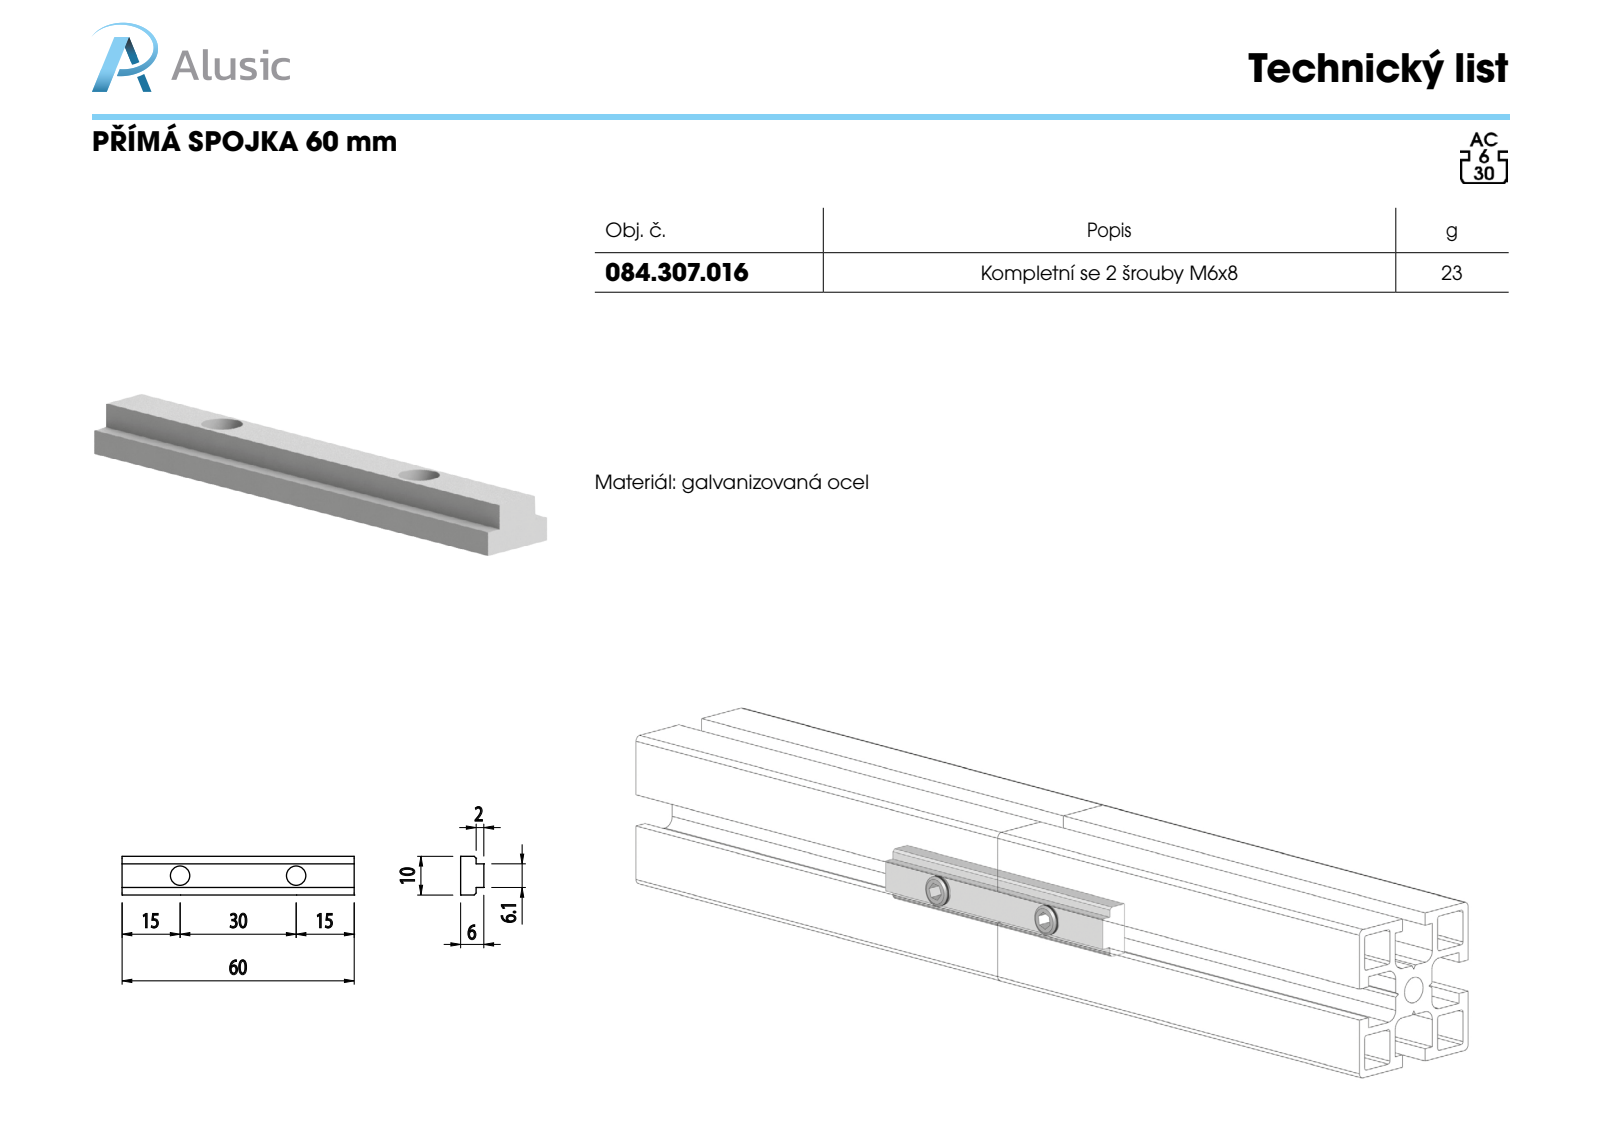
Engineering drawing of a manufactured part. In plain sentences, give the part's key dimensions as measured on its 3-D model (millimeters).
The part is named "084.307.016". Its 3-D file was written by "SolidWorks 2011 (CONFIG_CONTROL_DESIGN)". It is 1 solid with 16 faces: 12 planar, 4 cylindrical and 0 other. Overall it measures 60 by 10 by 6 millimeters. Its volume is 2 881 cubic millimeters and its surface area 2 099 square millimeters. Round holes: 2 of diameter 5. The main face-to-face distances are 6, 1.95, 8.05, 10, 4, 2, 6.1, 60. The hole center spacings are 30.
